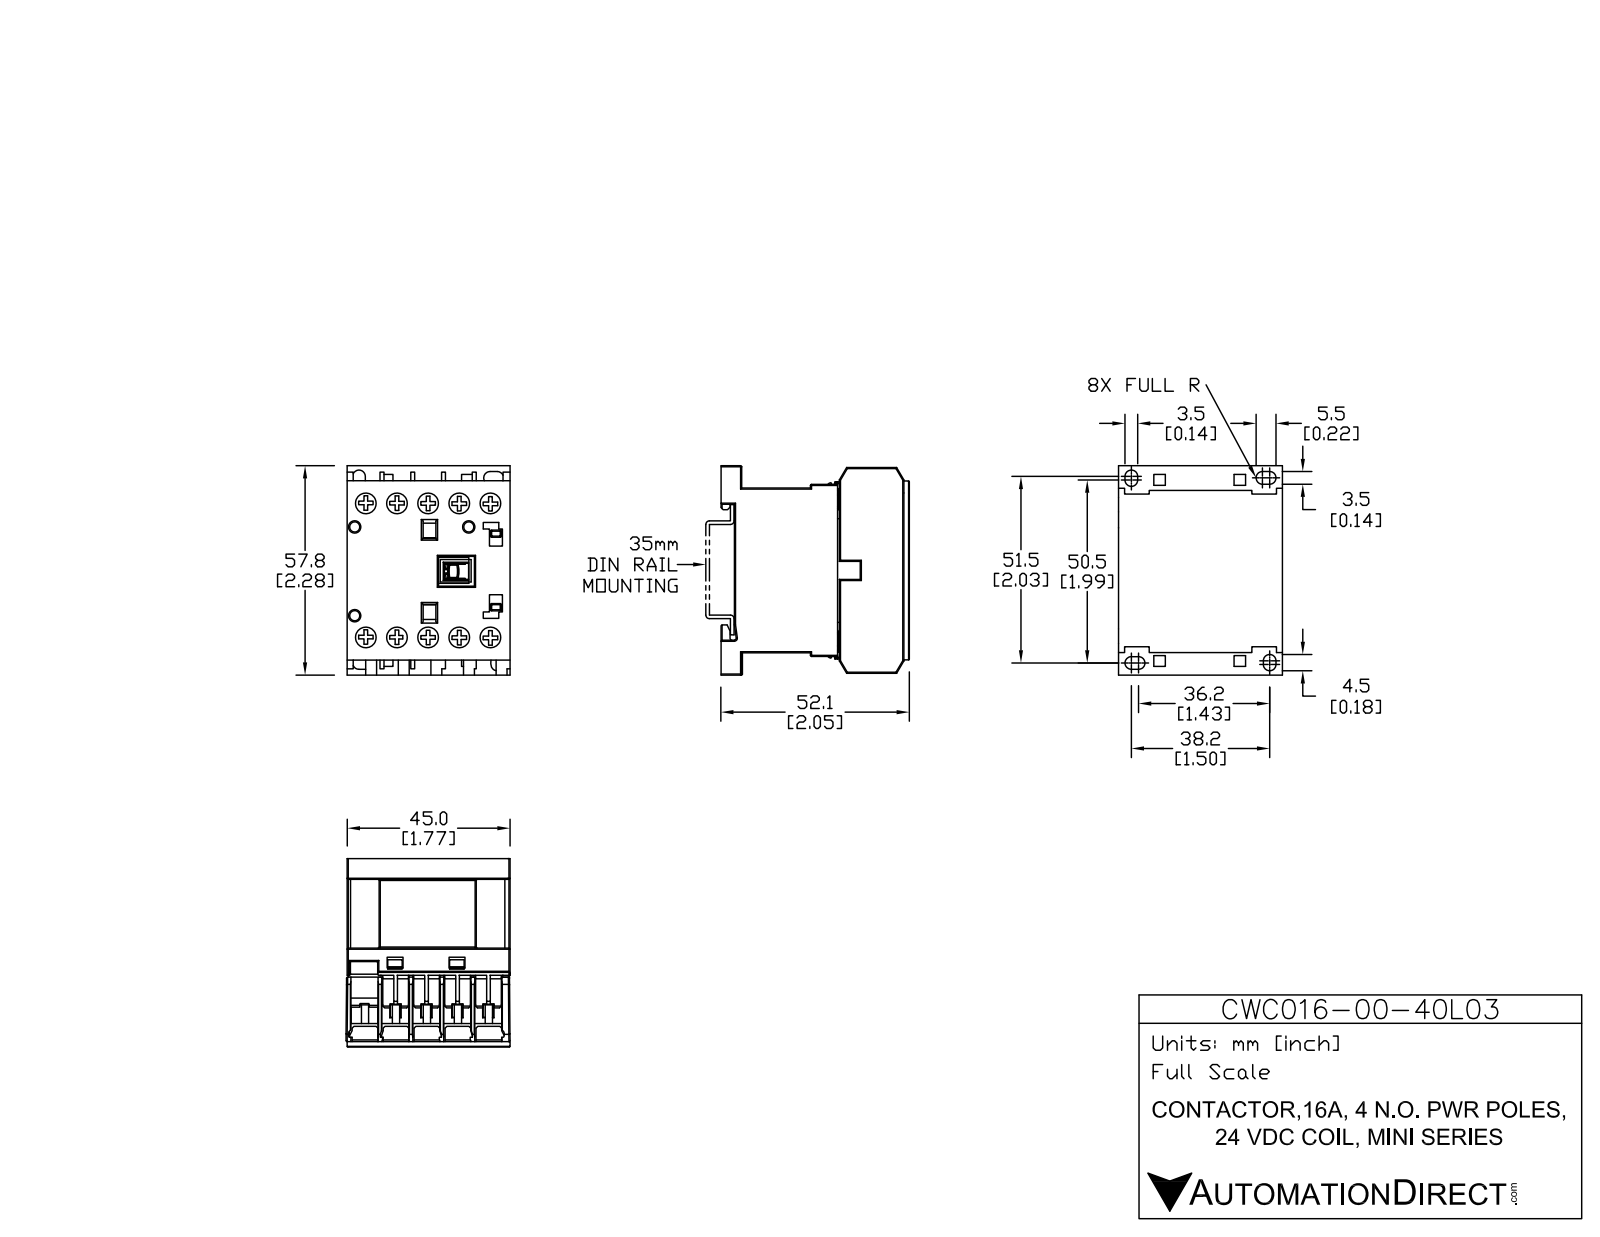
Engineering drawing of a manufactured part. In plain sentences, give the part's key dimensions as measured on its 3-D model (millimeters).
The part is named "CWC16-00-40L03". Its 3-D file was written by "SolidWorks 2013 (AUTOMOTIVE_DESIGN)". It is 15 solids with 535 faces: 445 planar, 90 cylindrical and 0 other. Overall it measures 58.04 by 52.12 by 45.75 millimeters. Its volume is 97 133 cubic millimeters and its surface area 30 437 square millimeters. Round holes: 10 of diameter 6.2, 3 of diameter 2.8. Round bosses or shafts: 10 of diameter 5.9. Partial cylindrical surfaces (rounded edges, fillets, slot ends): 20 of radius 0.3, 6 of radius 1.72, 2 of radius 1.73, 1 of radius 0.32, 1 of radius 0.42, 1 of radius 0.55. The main face-to-face distances are 8.25, 45.5, 1.25, 16.5, 9.5, 5.5, 17.75, 5.13, 10.63, 7. The hole center spacings are 8.55, 37.94, 17.1, 40.72, 36.96, 25.65, 44.99, 6.91.
